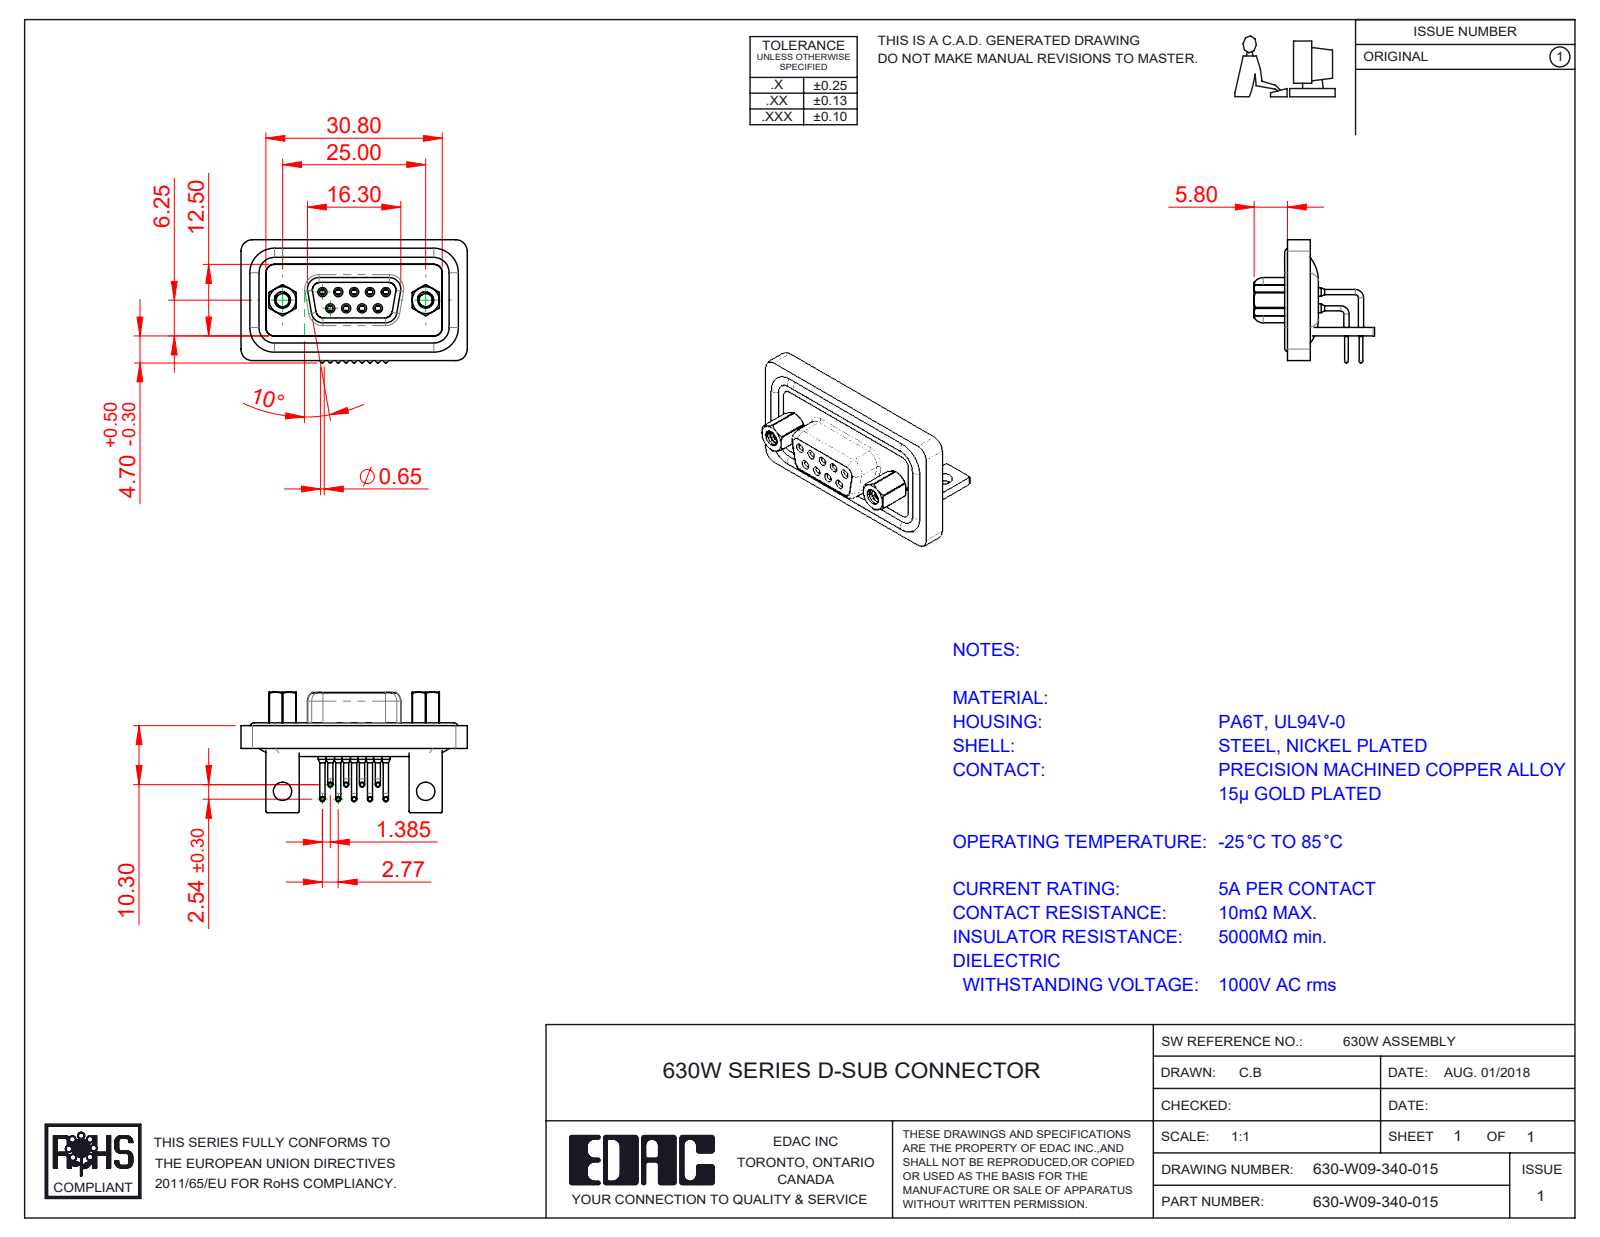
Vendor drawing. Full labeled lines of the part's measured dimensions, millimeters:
Part name (STEP PRODUCT): 630W 4-40 Threaded Rivet_Stabilizer; 630W Contact Row 2; 630W Contact Row 1; 630W Shell_09 Contacts (+5 more)
STEP written by: SolidWorks 2016 (CONFIG_CONTROL_DESIGN)
Units: millimetres
Bodies: 19 solids, 964 faces (258 planar, 465 cylindrical, 241 other)
Overall size (bounding box): 39.51 × 21.5 × 21.05
Volume: 4 726 mm³ · Surface area: 8 077 mm²
Round holes (diameter × count): ⌀1 ×9, ⌀1.1 ×9, ⌀1.5 ×9, ⌀1.7 ×9, ⌀1.8 ×9, ⌀2 ×9, ⌀2.26 ×2, ⌀2.29 ×2, ⌀3.2 ×2, ⌀4 ×2, ⌀4.8 ×2, ⌀4.9 ×2
Round bosses / shafts (diameter × count): ⌀0.9 ×18, ⌀1.6 ×13, ⌀0.65 ×9, ⌀1.5 ×4, ⌀2.79 ×2, ⌀5 ×1
Partial cylindrical surfaces — rounded edges, fillets, slot ends (radius × count): R2 ×15, R1.5 ×14, R0.25 ×12, R1.35 ×8, R2.7 ×6, R0.5 ×5, R0.9 ×4, R1.6 ×4
Main face-to-face distances: 0.4, 1.6, 1.1, 1.8, 2.9, 2.5, 4.3, 5.8, 1.5, 0.5
Hole centre spacings: 3.16, 2.77, 5.54, 5.03, 5.04, 7.48, 7.49, 8.31
